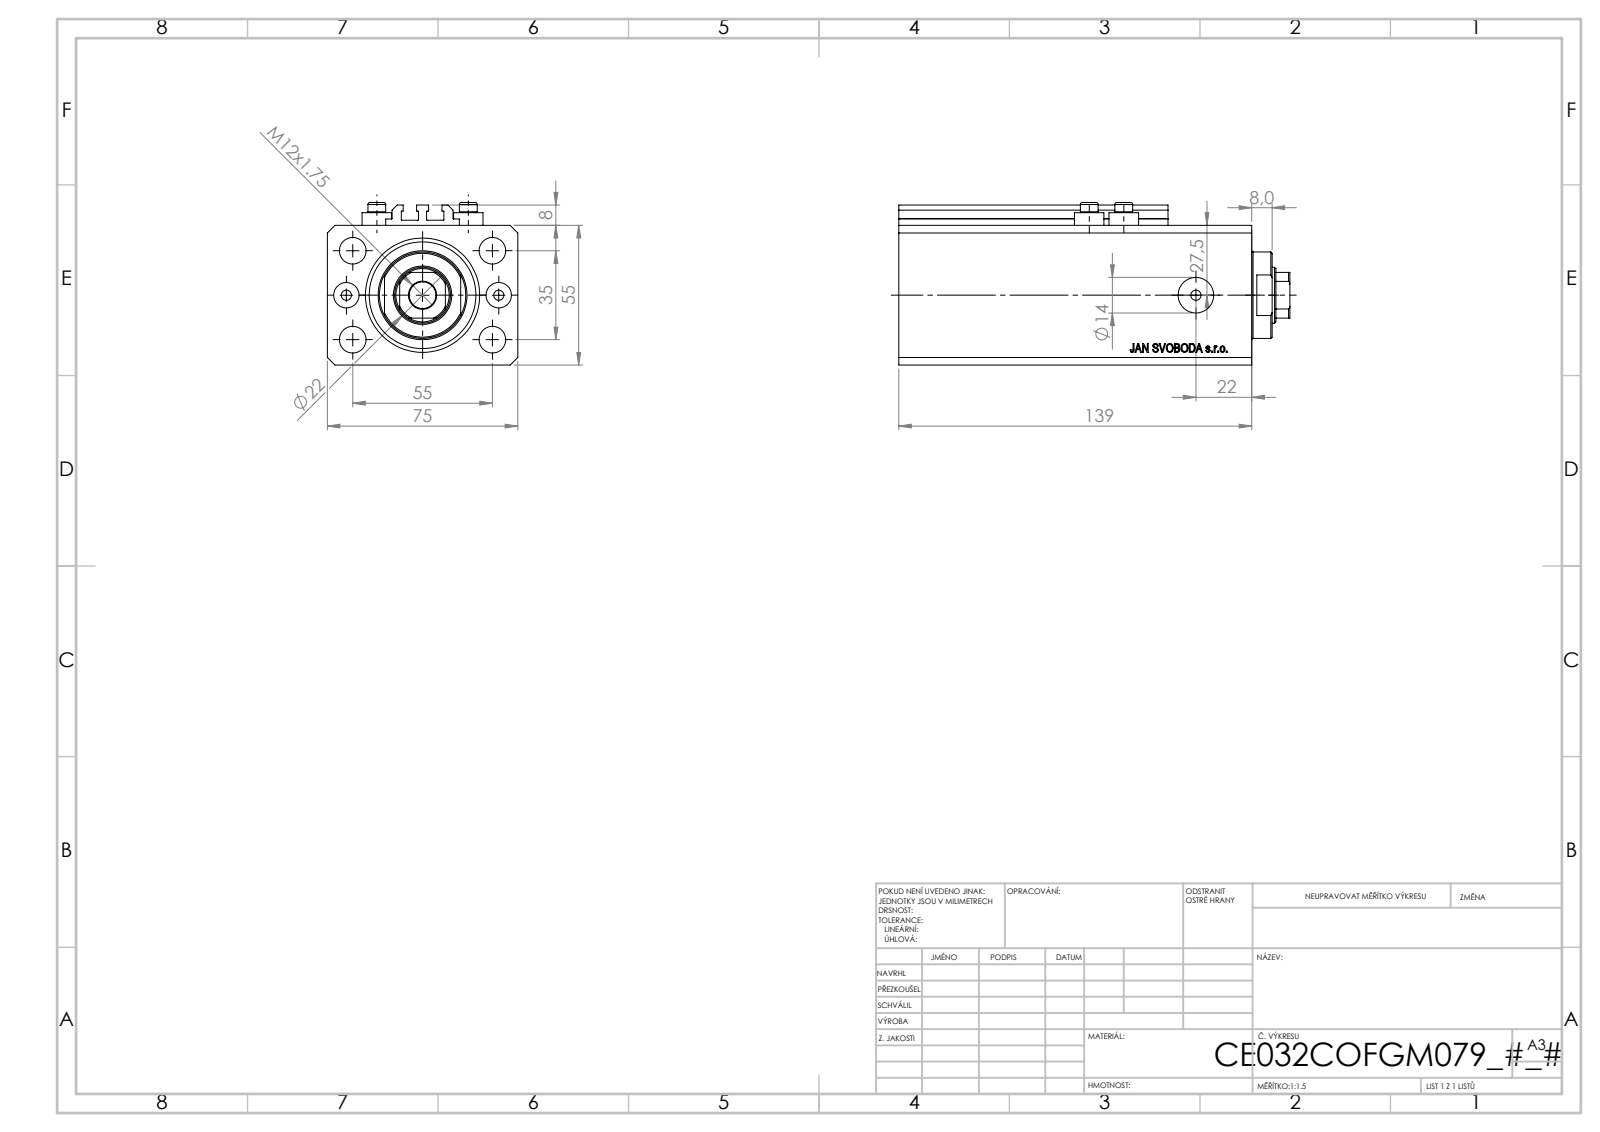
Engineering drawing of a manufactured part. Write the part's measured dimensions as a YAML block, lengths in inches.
part_name: "V250CE_C_VCP; ALLEN BOLT V250CE; V250CE_VC_C; V250CE_C_Body"
step_written_by: "SolidWorks 2019 (CONFIG_CONTROL_DESIGN)"
units: inches
bodies: {solids: 8, faces: 1034, planar: 504, cylindrical: 86, other: 444}
overall_size: [6.063, 2.953, 2.52]
volume: 31.08
surface_area: 170.7
round_holes:
  - {diameter: 0.157, count: 8}
  - {diameter: 0.413, count: 5}
  - {diameter: 0.394, count: 2}
  - {diameter: 0.551, count: 2}
  - {diameter: 0.866, count: 1}
  - {diameter: 1.26, count: 1}
  - {diameter: 1.772, count: 1}
round_bosses_or_shafts:
  - {diameter: 0.457, count: 4}
  - {diameter: 0.276, count: 4}
  - {diameter: 1.339, count: 1}
partial_cylinders:
  - {radius: 0.008, count: 10}
  - {radius: 0.413, count: 1}
face_to_face_distances: [2.165, 2.953, 5.472, 0.591, 4.882, 0.39, 4.492, 5.083, 0.098, 0.079]
hole_center_spacings: [0.696, 1.283, 2.366, 0.535, 1.181, 1.378, 1.417, 1.515]
